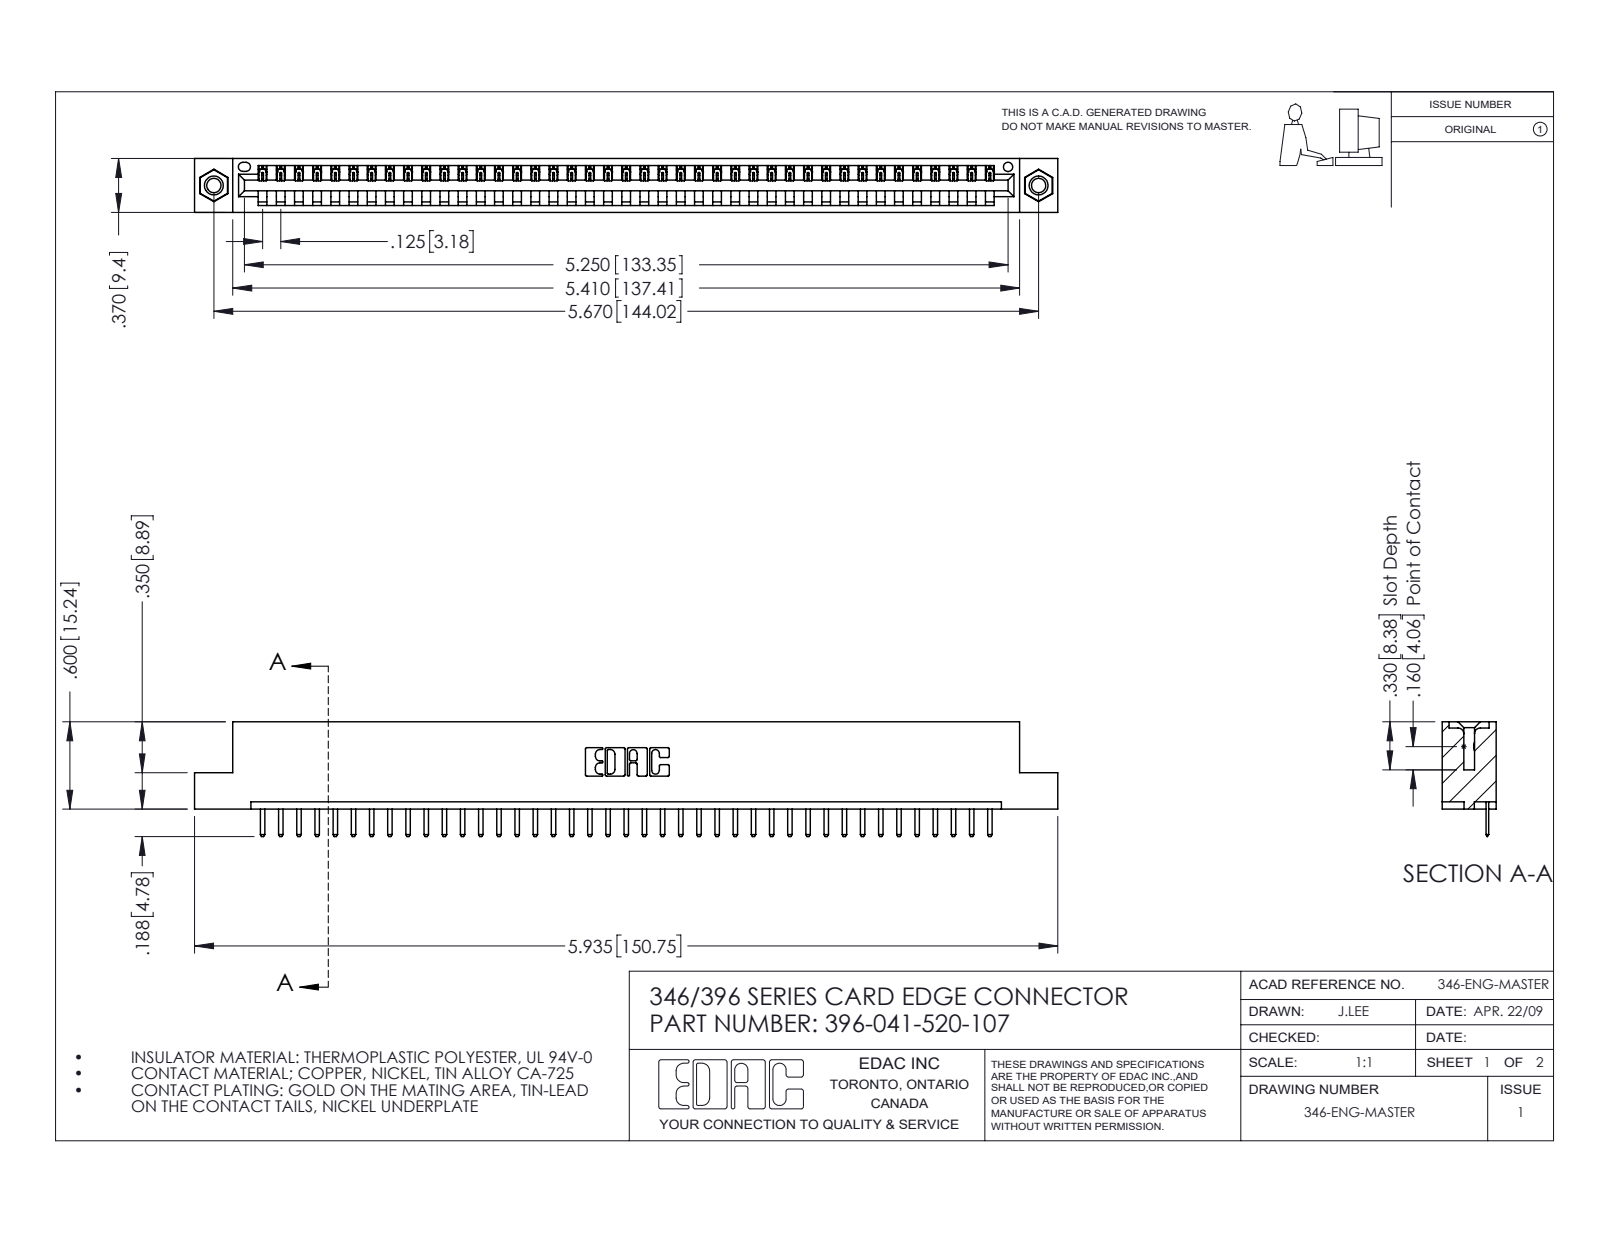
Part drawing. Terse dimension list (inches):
name: 345-250-001_345-250-005-103; 345-292-001_345-293-120; 346 Part_Flush Mounting Lugs - 0.156 Dia-TI; 396-041-520-107
written by: SolidWorks 2016 (CONFIG_CONTROL_DESIGN)
unit: in
bodies: 44 solids, 2724 faces (1830 planar, 878 cylindrical, 16 other)
size: 5.935 × 0.788 × 0.37
volume: 0.872 in³; area: 27.11 in²
holes: 2× ⌀0.098, 2× ⌀0.125, 2× ⌀0.156, 1× ⌀0.064
bosses: 2× ⌀0.155
rounds: 84× R0.01, 82× R0.006, 22× R0.01, 6× R0.007, 6× R0.031, 3× R0.026, 2× R0.031, 2× R0.04
face distances: 0.048, 0.322, 0.37, 0.25, 0.148, 0.222, 0.1, 0.174, 0.072, 0.298
hole spacings: 0.246, 5.461, 5.67
